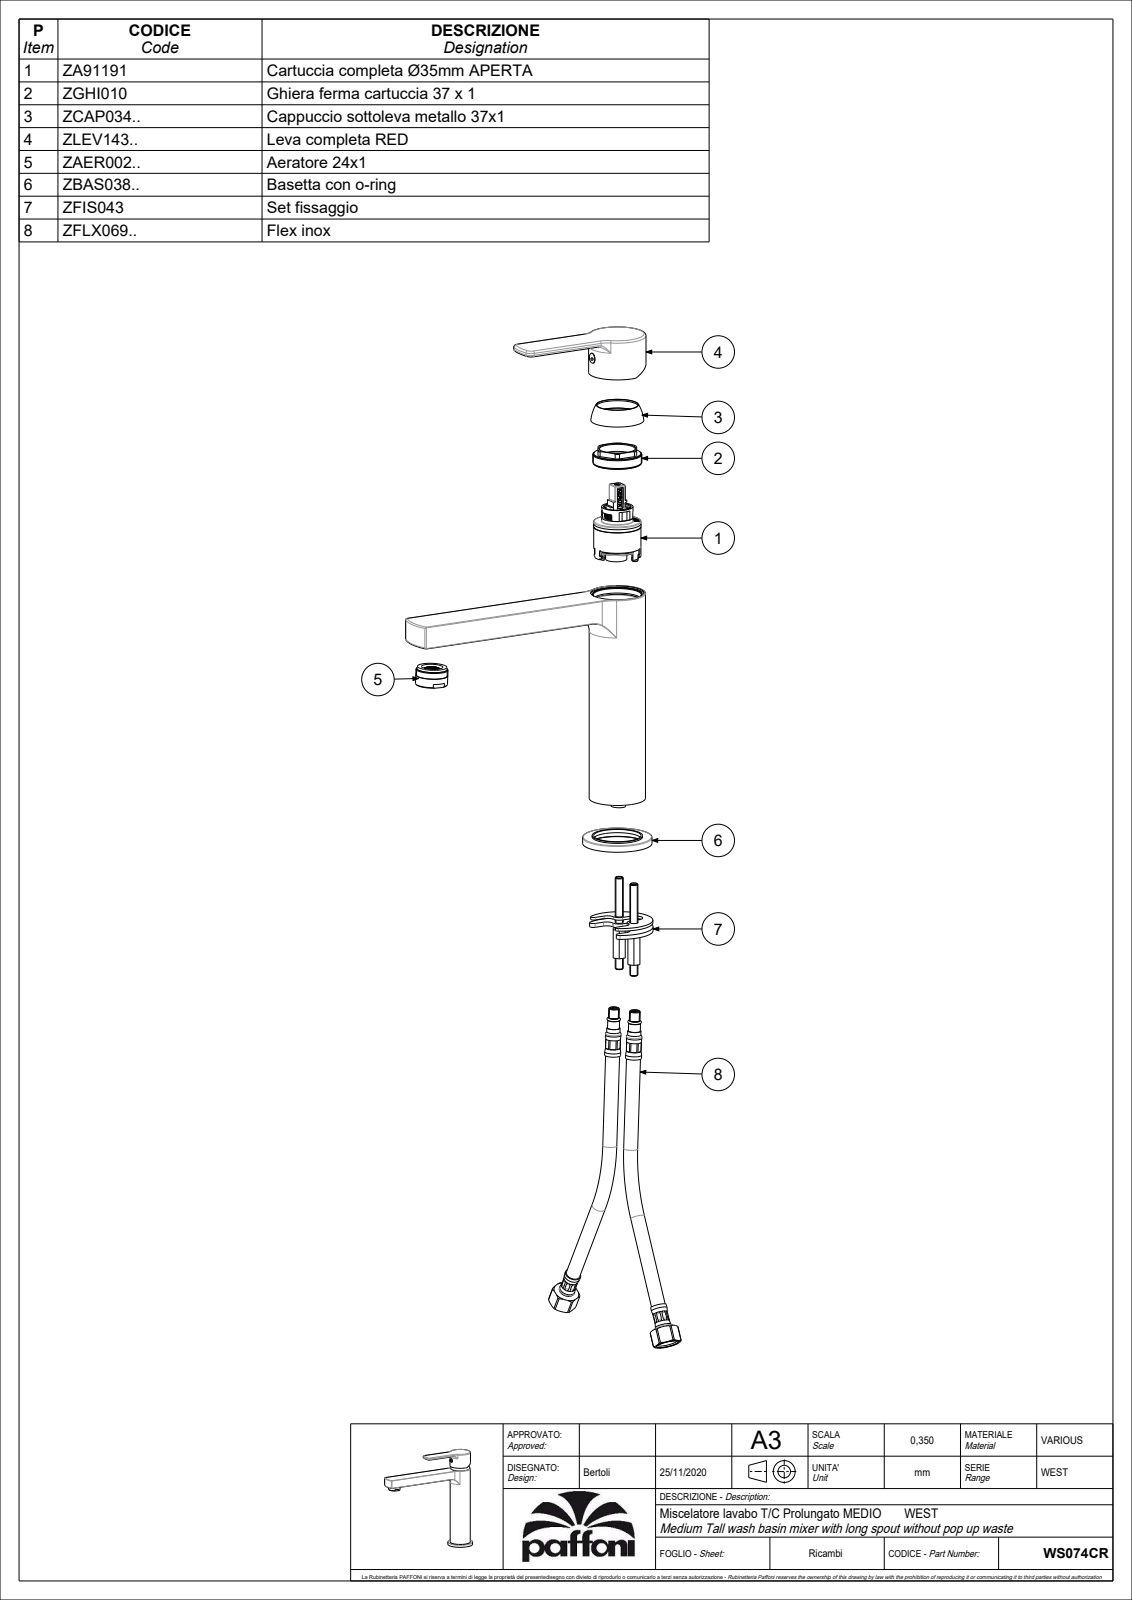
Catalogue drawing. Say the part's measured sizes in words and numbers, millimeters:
The part is named "WS074CR". Its 3-D file was written by "CREO PARAMETRIC BY PTC INC, 2020044 (CONFIG_CONTROL_DESIGN)". It is 3 solids with 3429 faces: 2436 planar, 569 cylindrical and 424 other. Overall it measures 203.5 by 200.55 by 52 millimeters. Its volume is 173 590 cubic millimeters and its surface area 126 098 square millimeters. Round holes: 4 of diameter 6, 4 of diameter 8.2, 3 of diameter 4, 2 of diameter 5, 2 of diameter 5.5, 2 of diameter 6.5, 2 of diameter 7, 2 of diameter 8, 2 of diameter 9, 1 of diameter 3, 1 of diameter 3.4, 1 of diameter 3.5. Round bosses or shafts: 6 of diameter 8, 2 of diameter 11, 2 of diameter 8.9, 2 of diameter 6.5, 2 of diameter 6, 2 of diameter 4.8, 2 of diameter 4, 1 of diameter 52. Partial cylindrical surfaces (rounded edges, fillets, slot ends): 89 of radius 0.5, 16 of radius 1.5, 14 of radius 1, 6 of radius 1.7, 5 of radius 2, 4 of radius 0.8, 4 of radius 5.8, 3 of radius 12.75. The main face-to-face distances are 3, 14, 17, 27, 30, 11, 53.05, 36.05, 39.05, 50.05. The hole center spacings are 14, 13.6, 2.83, 8.6, 9.26, 11.77, 13.45, 15.13.
